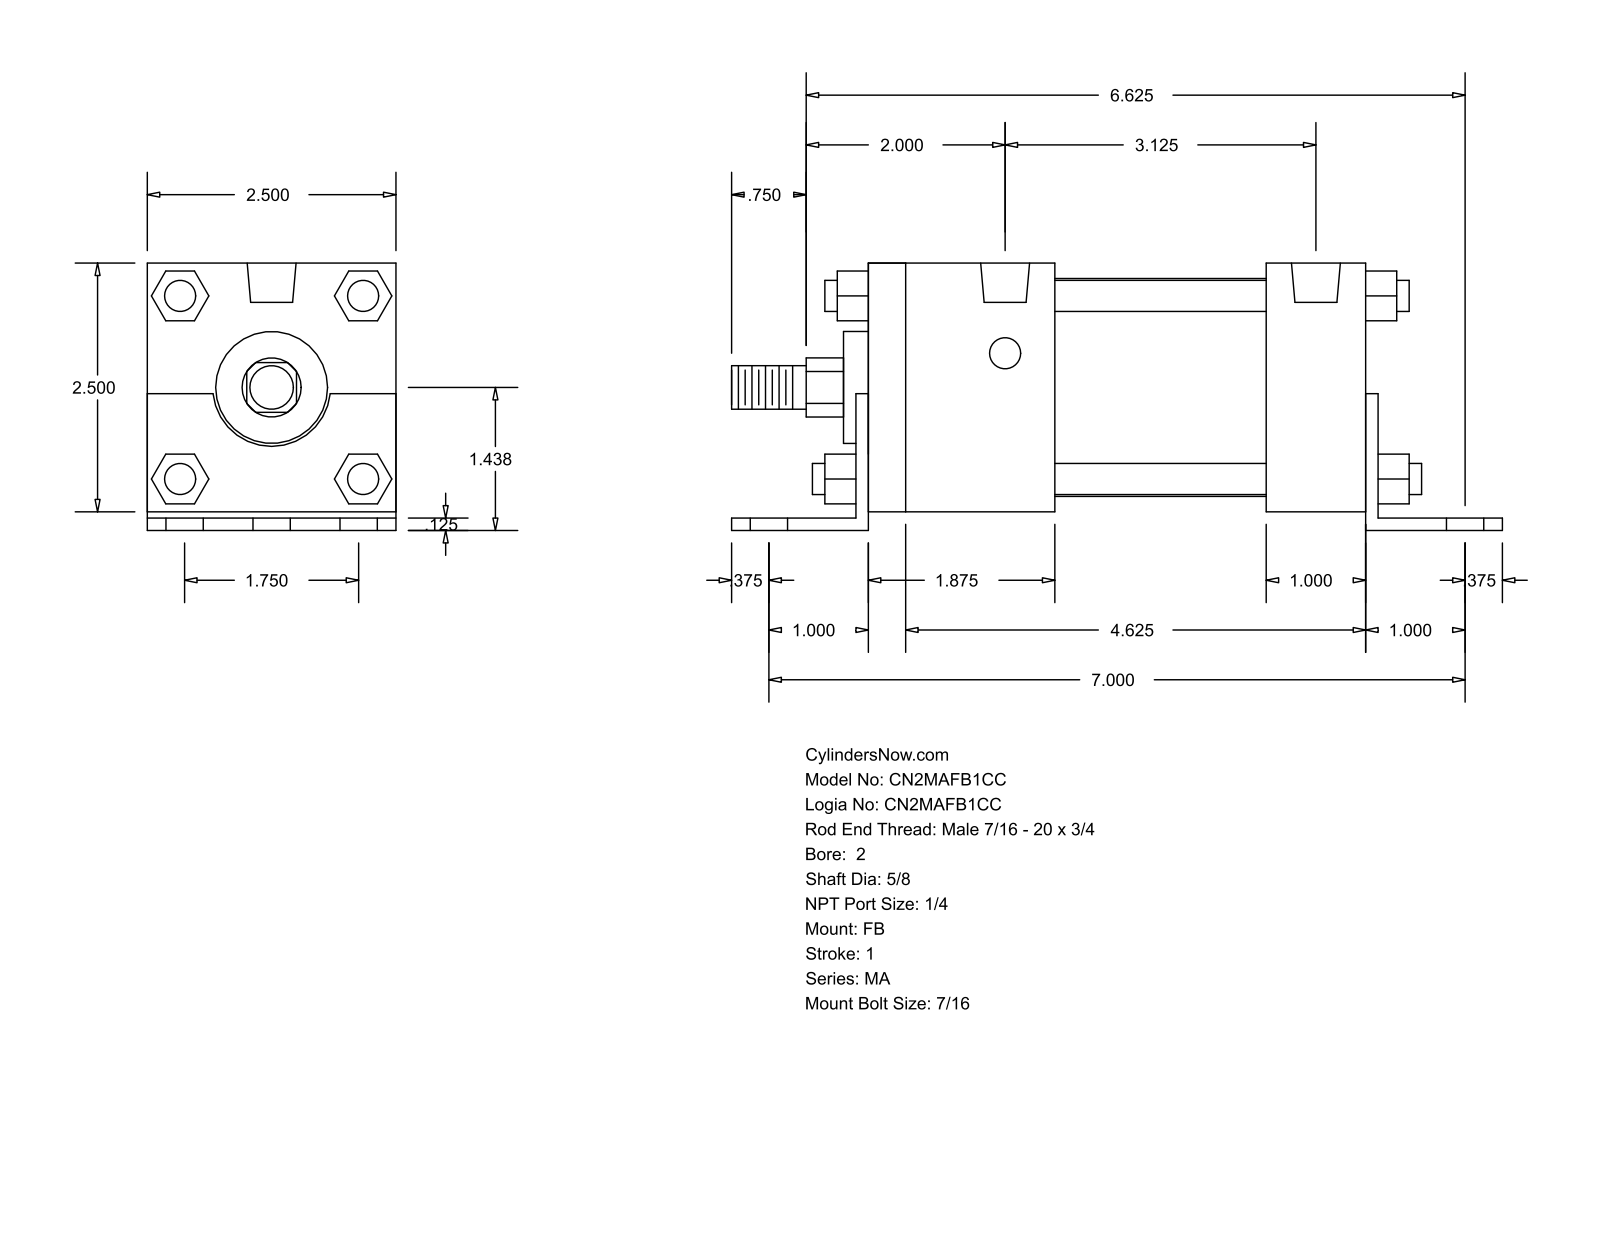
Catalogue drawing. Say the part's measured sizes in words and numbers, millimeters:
The part is named "MA_FB__0200_0.625". Its 3-D file was written by "GSSL Pune (CONFIG_CONTROL_DESIGN)". It is 0 solids with 140 faces: 105 planar, 35 cylindrical and 0 other. Overall it measures 196.85 by 68.26 by 63.5 millimeters. Round holes: 6 of diameter 11.11, 4 of diameter 7.94, 2 of diameter 12.49. Round bosses or shafts: 4 of diameter 7.94, 1 of diameter 55.63, 1 of diameter 28.57, 1 of diameter 15.88, 1 of diameter 11.11. Partial cylindrical surfaces (rounded edges, fillets, slot ends): 1 of radius 7.54, 1 of radius 15.05. The main face-to-face distances are 63.5, 3.17, 4.76, 68.26, 1.59, 65.09, 133.35, 53.97, 3.18, 127. The hole center spacings are 22.23, 179.19, 177.81, 44.11, 44.46, 64.3, 79.38, 119.56.
